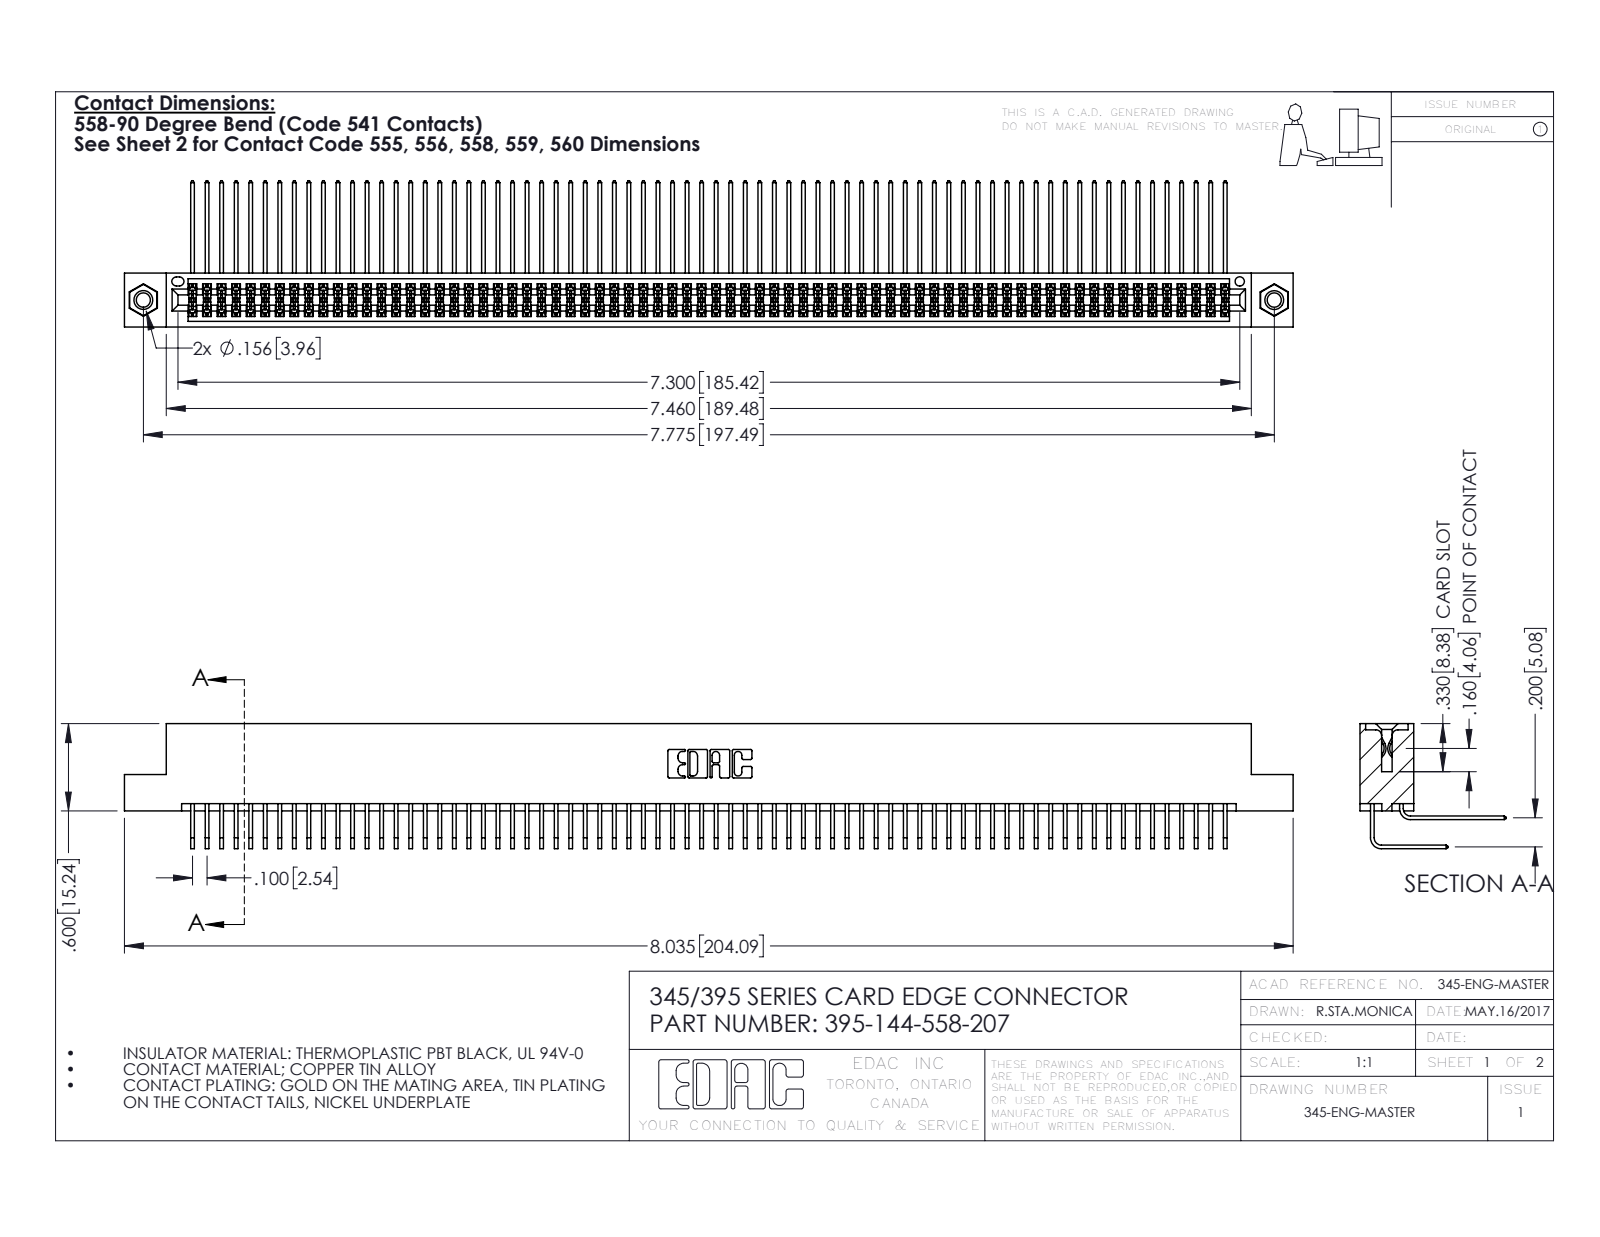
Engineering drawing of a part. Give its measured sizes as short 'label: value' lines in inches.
name: 395-144-558-207; 345-250-001_345-250-005-103; 345 Part_Flush Mounting Lugs - 0.156 Dia-TI; 345-292-001_558 559 Tail - 1 (+1 more)
written by: SolidWorks 2016 (CONFIG_CONTROL_DESIGN)
unit: in
bodies: 147 solids, 7674 faces (5152 planar, 2506 cylindrical, 16 other)
size: 8.035 × 1.005 × 0.859
volume: 1.277 in³; area: 54.93 in²
holes: 2× ⌀0.098, 2× ⌀0.125, 2× ⌀0.156, 1× ⌀0.064
bosses: 2× ⌀0.155
rounds: 216× R0.006, 22× R0.01, 6× R0.007, 6× R0.031, 3× R0.026, 2× R0.014, 2× R0.019, 2× R0.022
face distances: 0.072, 0.298, 0.2, 0.37, 0.098, 0.272, 0.025, 0.225, 0.025, 0.175
hole spacings: 0.27, 7.539, 7.775
